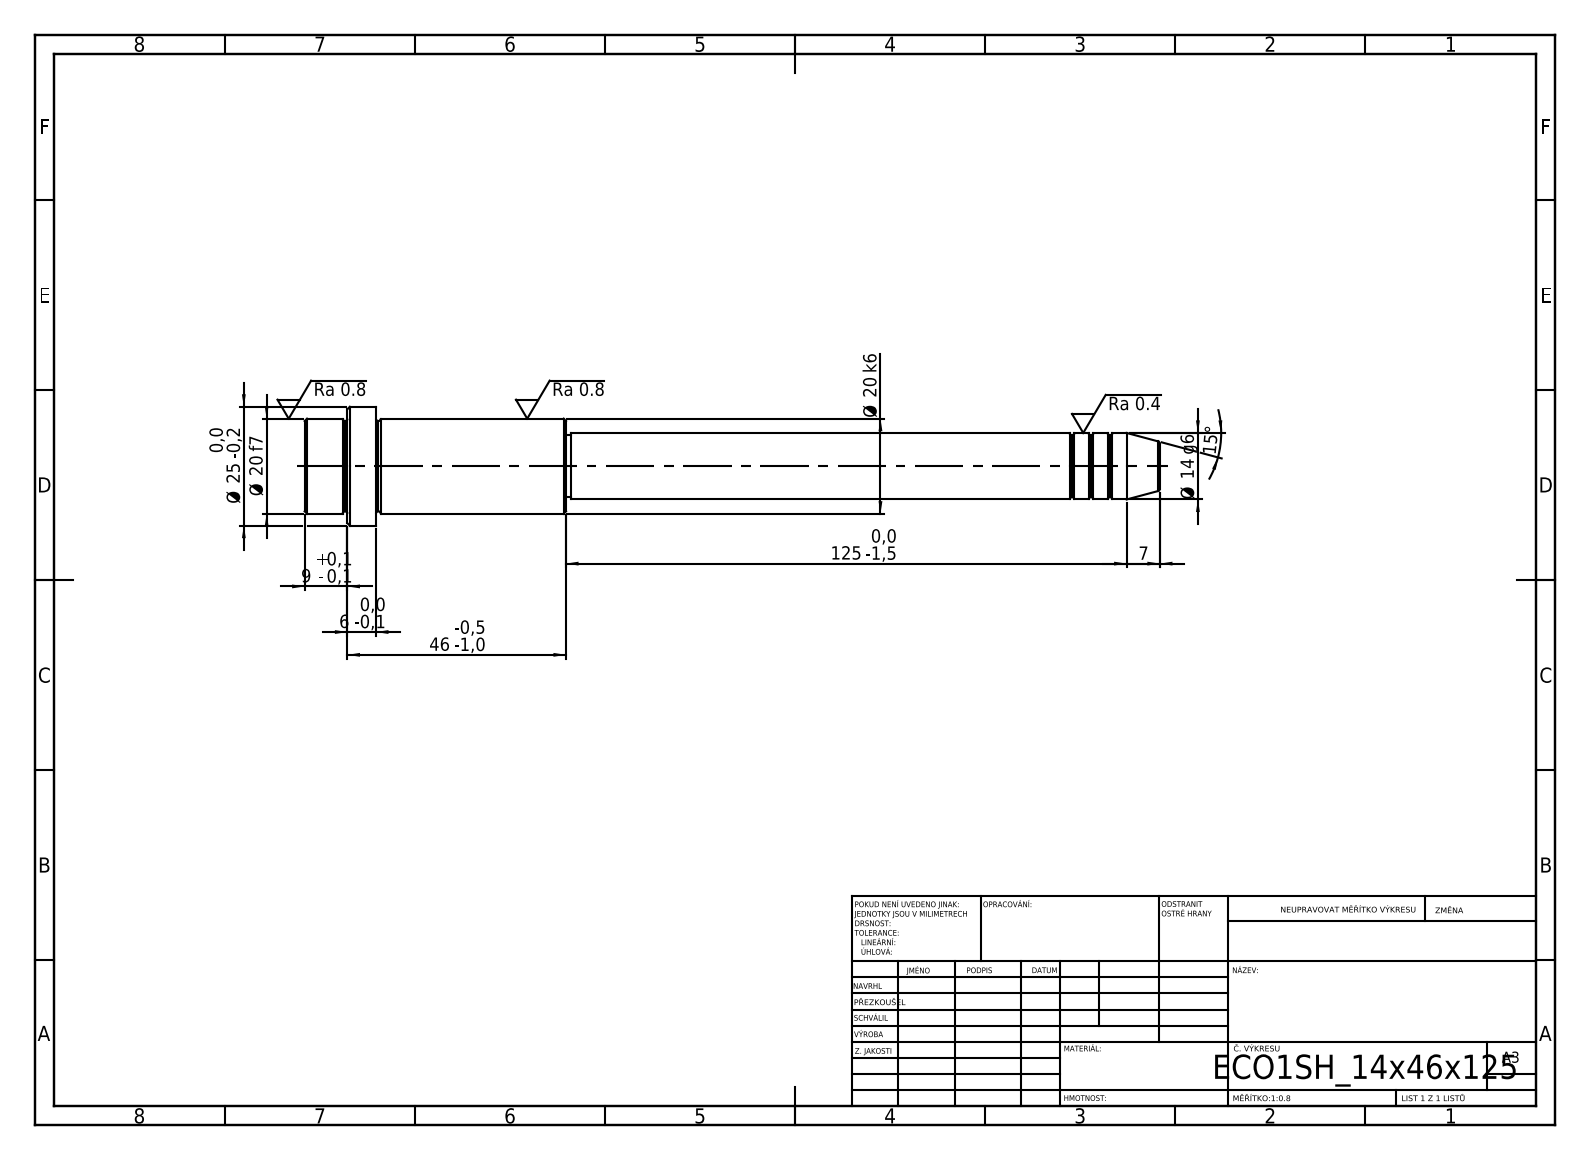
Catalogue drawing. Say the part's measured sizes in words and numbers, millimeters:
Its 3-D file was written by "SolidWorks 2019 (CONFIG_CONTROL_DESIGN)". It is 1 solid with 52 faces: 6 planar, 16 cylindrical and 30 other. Overall it measures 180 by 25 by 25 millimeters. Its volume is 37 173 cubic millimeters and its surface area 10 032 square millimeters. Round bosses or shafts: 1 of diameter 25, 1 of diameter 20, 1 of diameter 14, 1 of diameter 13. The main face-to-face distances are 15, 40, 55, 46, 6, 9, 125, 165, 171, 180.
